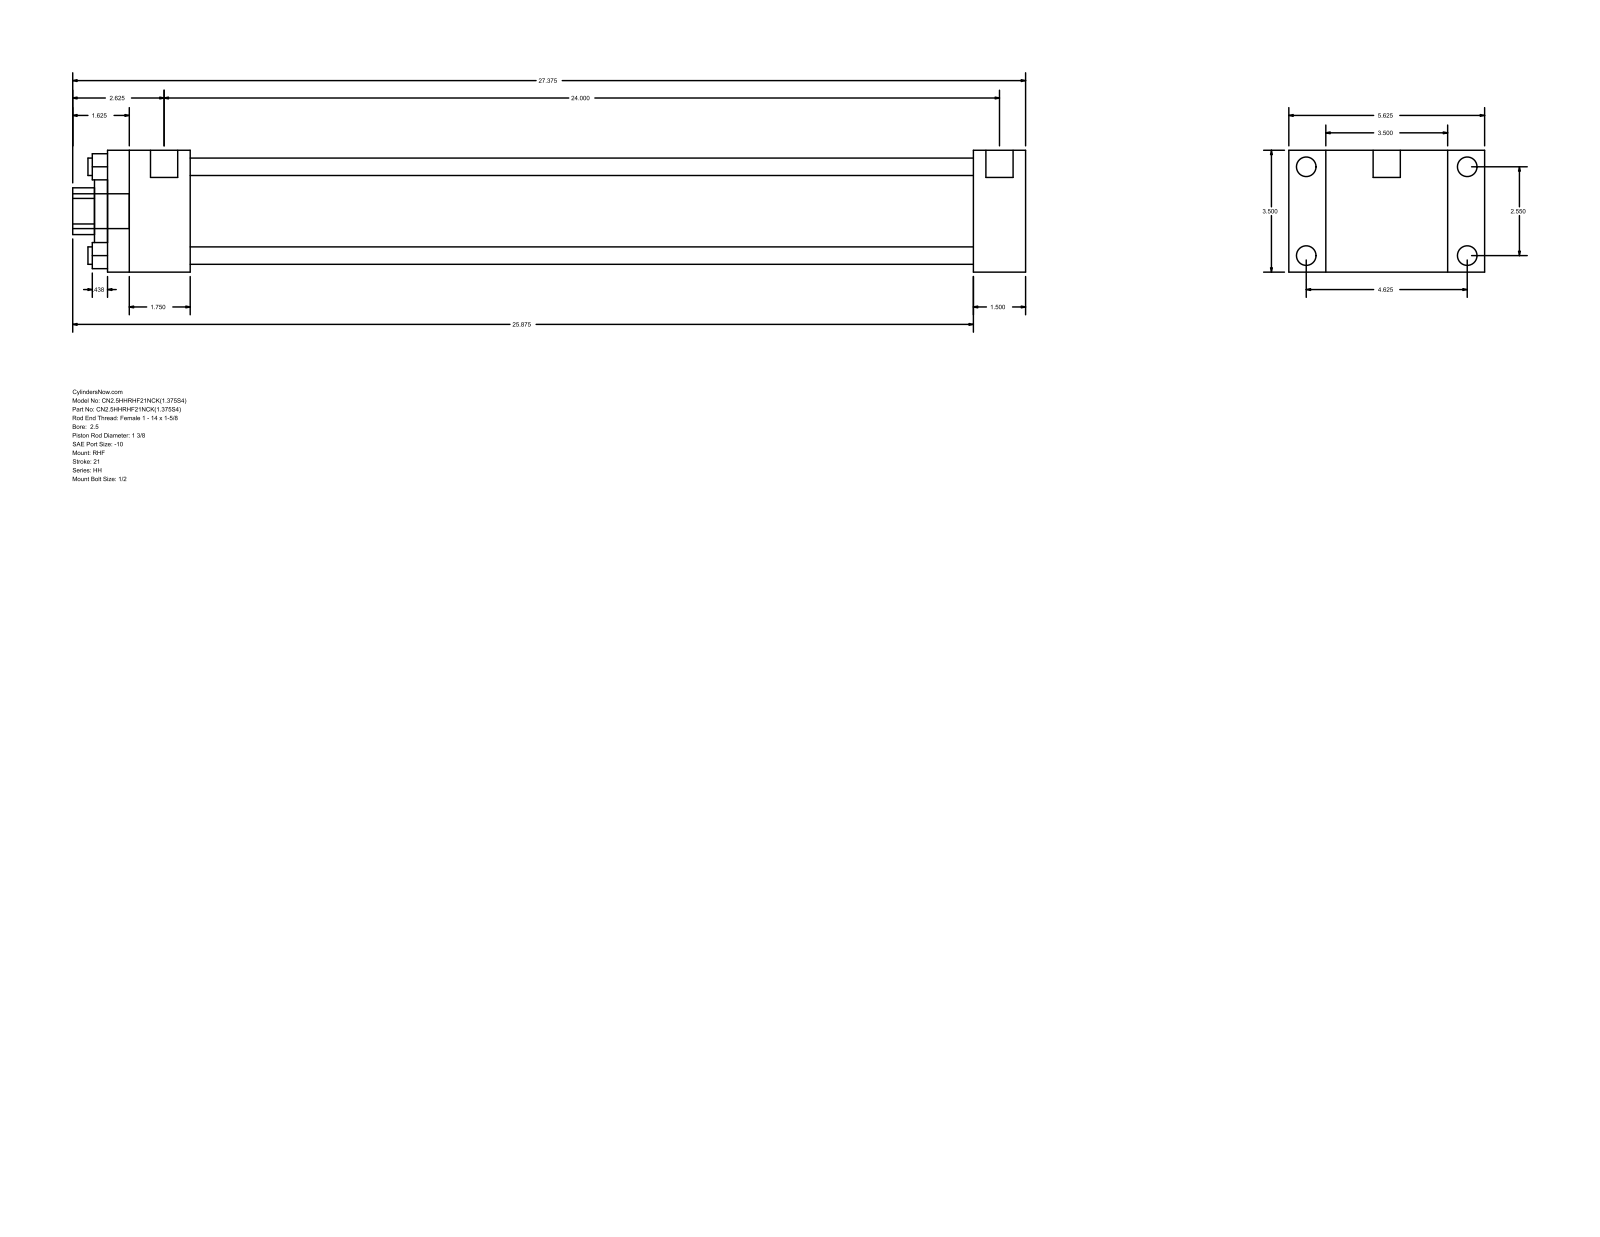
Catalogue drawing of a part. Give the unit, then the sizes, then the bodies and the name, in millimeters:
Units: millimetres
Overall size (bounding box): 695.33 × 142.88 × 88.9
Round holes (diameter × count): ⌀12.7 ×4, ⌀34.92 ×1, ⌀50.8 ×1, ⌀73.03 ×1
Round bosses / shafts (diameter × count): ⌀14.3 ×4, ⌀5.56 ×4, ⌀19.84 ×2, ⌀25.4 ×1
Partial cylindrical surfaces — rounded edges, fillets, slot ends (radius × count): R17.06 ×1
Main face-to-face distances: 88.9, 38.1, 26.99, 115.89, 631.83, 669.93, 142.88, 60.32, 571.51, 609.61
Hole centre spacings: 45.79, 64.76, 91.58
Bodies: 0 solids, 88 faces (60 planar, 28 cylindrical, 0 other)
Part name (STEP PRODUCT): HH_RHF__0250_1.375
STEP written by: GSSL Pune (CONFIG_CONTROL_DESIGN)
